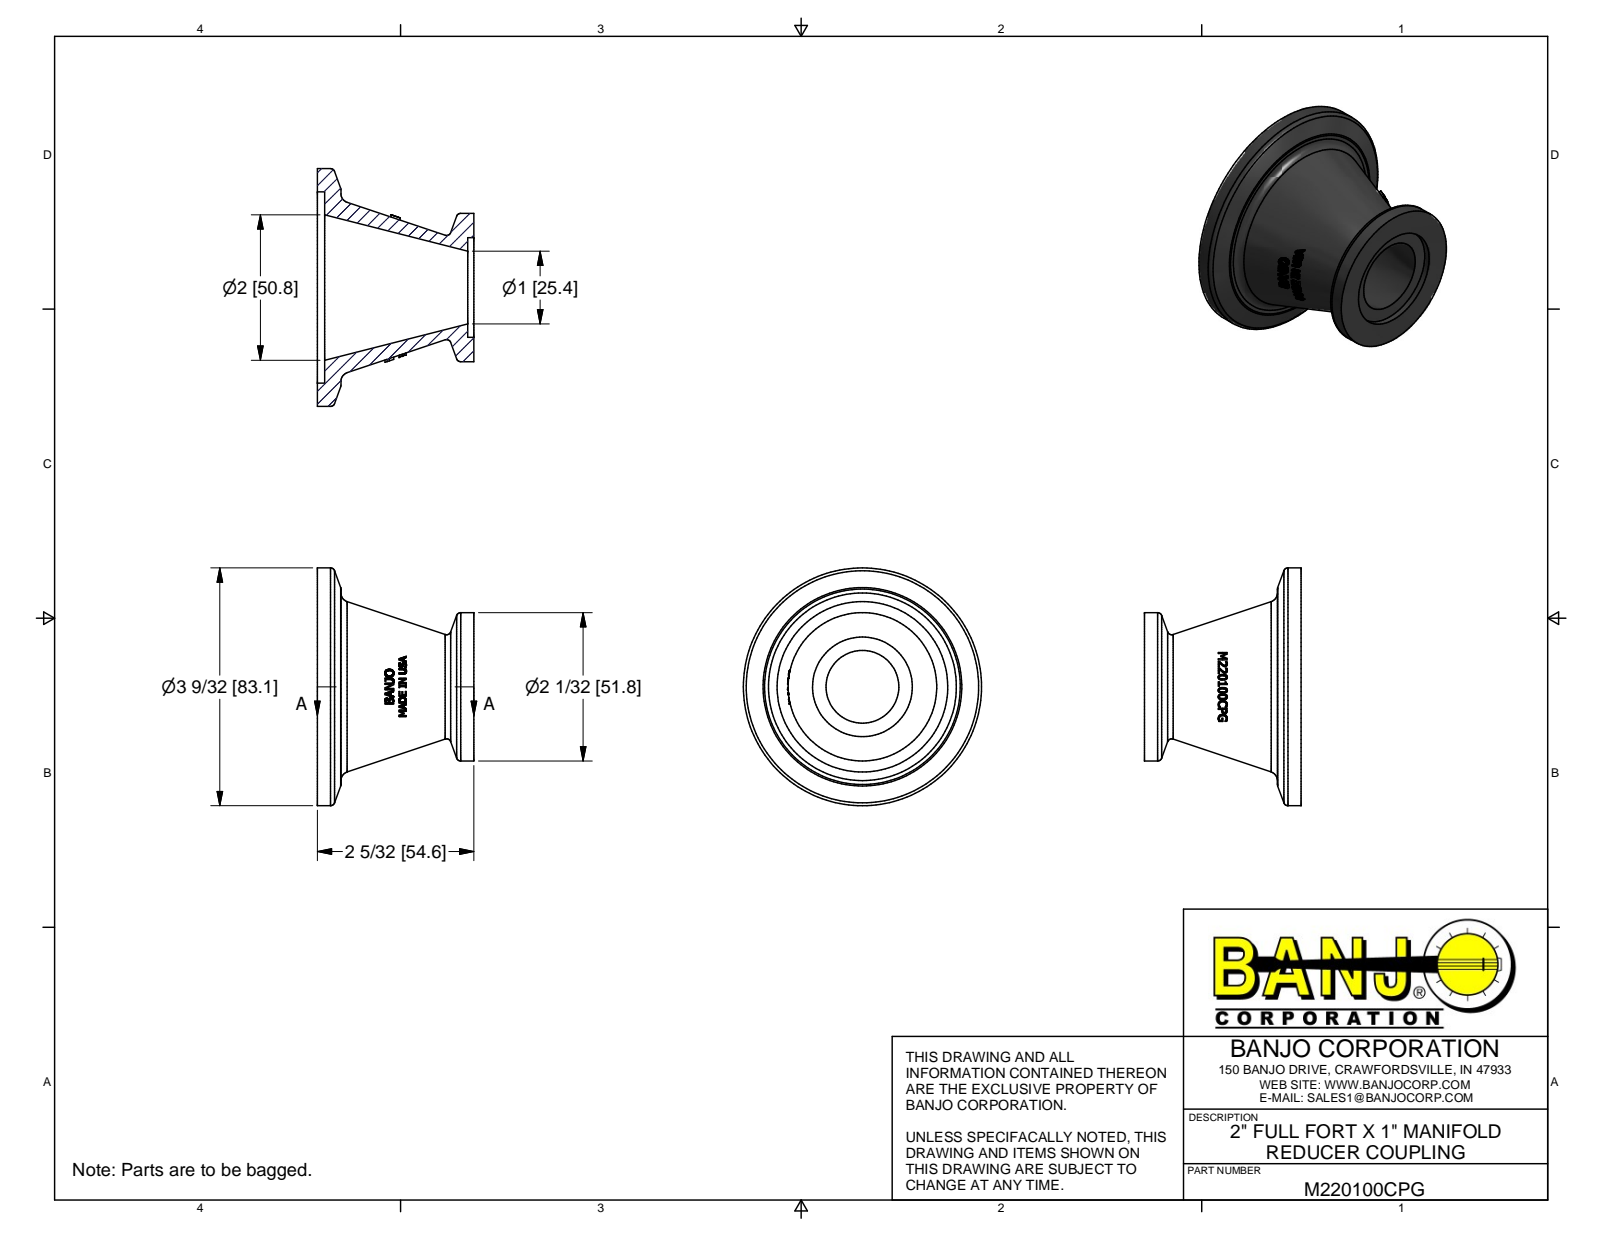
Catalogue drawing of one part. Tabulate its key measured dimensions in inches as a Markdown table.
| quantity | value |
| --- | --- |
| part name | M220100CPG |
| STEP written by | Autodesk Inventor 2012 (AUTOMOTIVE_DESIGN) |
| units | inches |
| bodies | 1 solid, 392 faces (182 planar, 4 cylindrical, 206 other) |
| overall size | 3.27 × 3.27 × 2.149 |
| volume | 3.639 in³ |
| surface area | 37.41 in² |
| round holes (diameter × count) | 1.37 × 1, 2.63 × 1 |
| round bosses / shafts (diameter × count) | 3.27 × 1, 2.04 × 1 |
| main face-to-face distances | 0.1, 2.149, 2.049, 0.084, 2.065, 1.965, 0.324, 0.224, 1.741, 1.825 |
